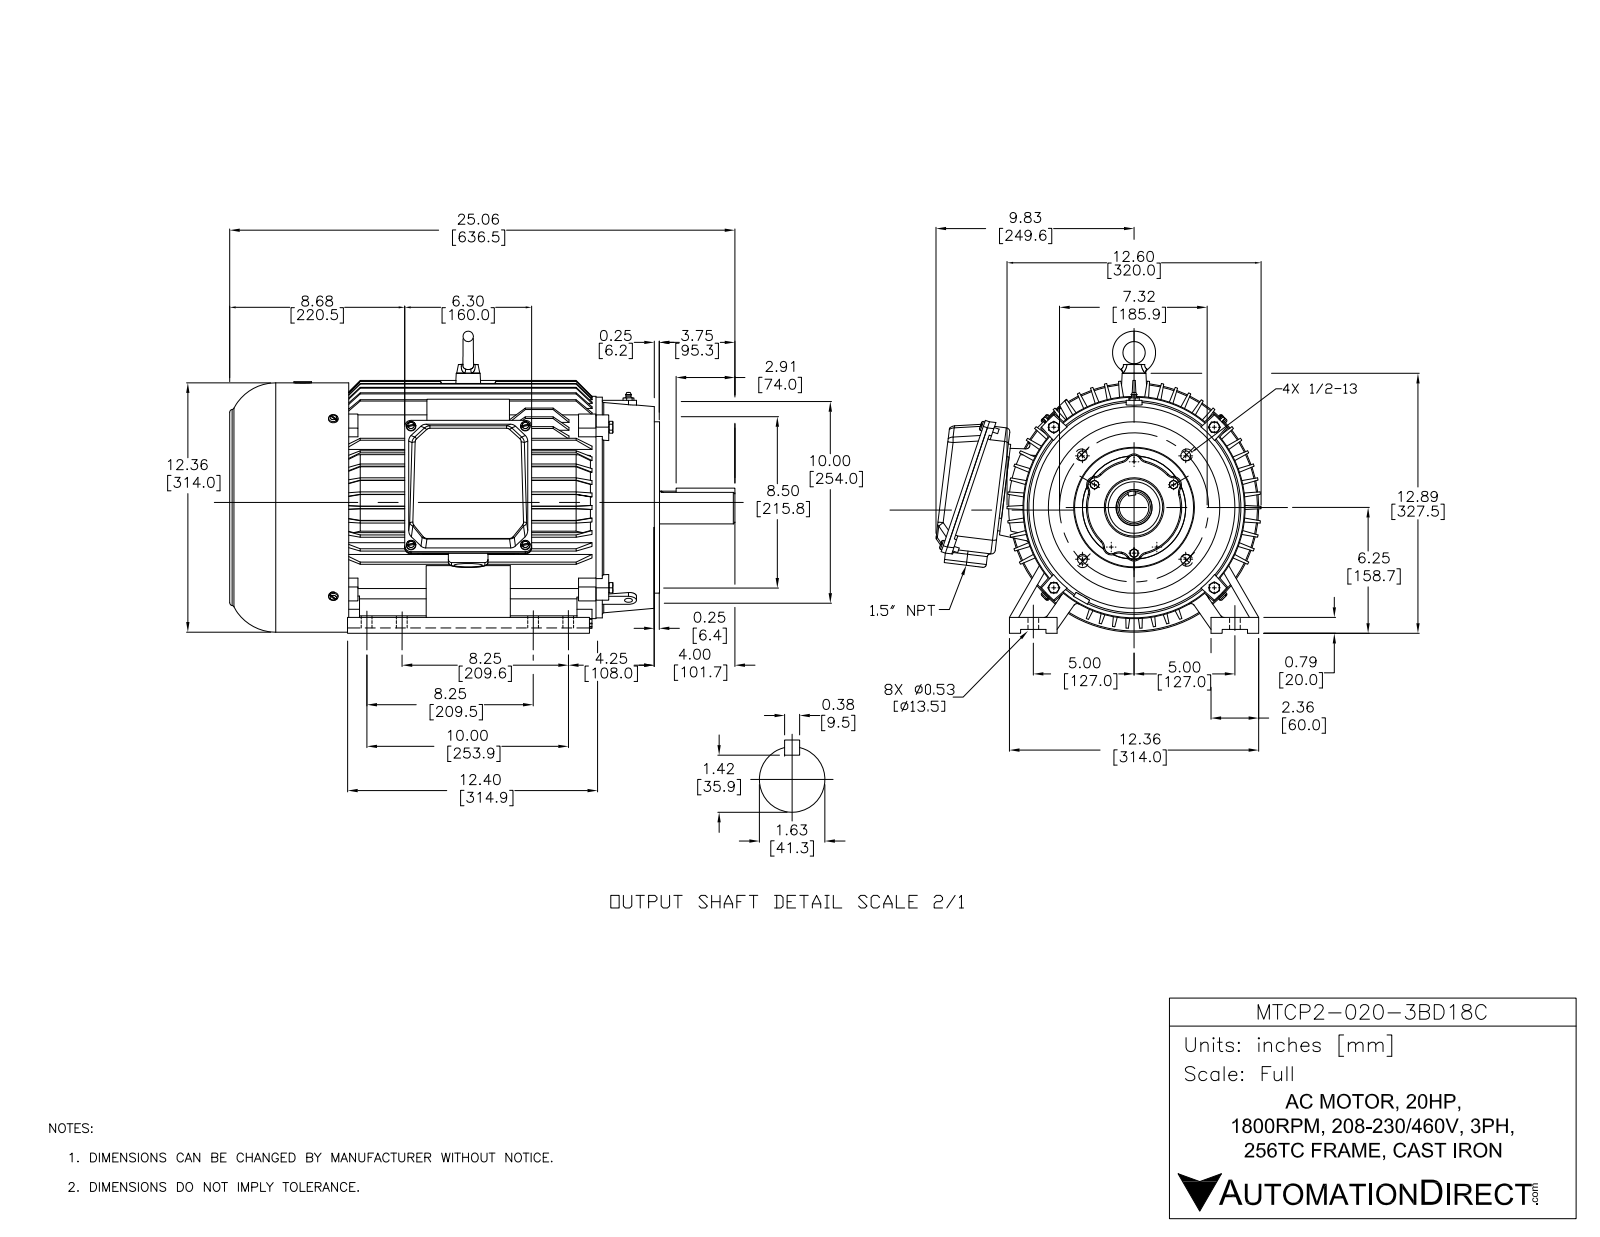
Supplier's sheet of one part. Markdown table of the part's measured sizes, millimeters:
| quantity | value |
| --- | --- |
| part name | PEWWE-256TC |
| STEP written by | SolidWorks 2017 (AUTOMOTIVE_DESIGN) |
| units | millimeters |
| bodies | 27 solids, 2295 faces (1379 planar, 479 cylindrical, 437 other) |
| overall size | 636.5 × 409.6 × 380.6 |
| volume | 10 370 000 mm³ |
| surface area | 2 310 000 mm² |
| round holes (diameter × count) | 7 × 14, 6 × 10, 8 × 8, 10 × 8, 14 × 8, 5 × 4, 12.5 × 4, 19 × 2, 2 × 1, 12 × 1, 36 × 1, 45.5 × 1 |
| round bosses / shafts (diameter × count) | 6 × 8, 314 × 1, 280 × 1, 278 × 1, 277.6 × 1, 263 × 1, 215.9 × 1, 135 × 1 |
| partial cylindrical surfaces (radius × count) | 10 × 55, 4 × 30, 5 × 14, 8 × 8, 3.5 × 7, 16 × 4, 0.1 × 2, 3 × 2 |
| main face-to-face distances | 5, 1.5, 20, 138, 374, 15, 71, 143, 538.5, 540 |
| hole center spacings | 75, 170, 57.5, 106.1, 254, 44.5, 51, 120.4 |
